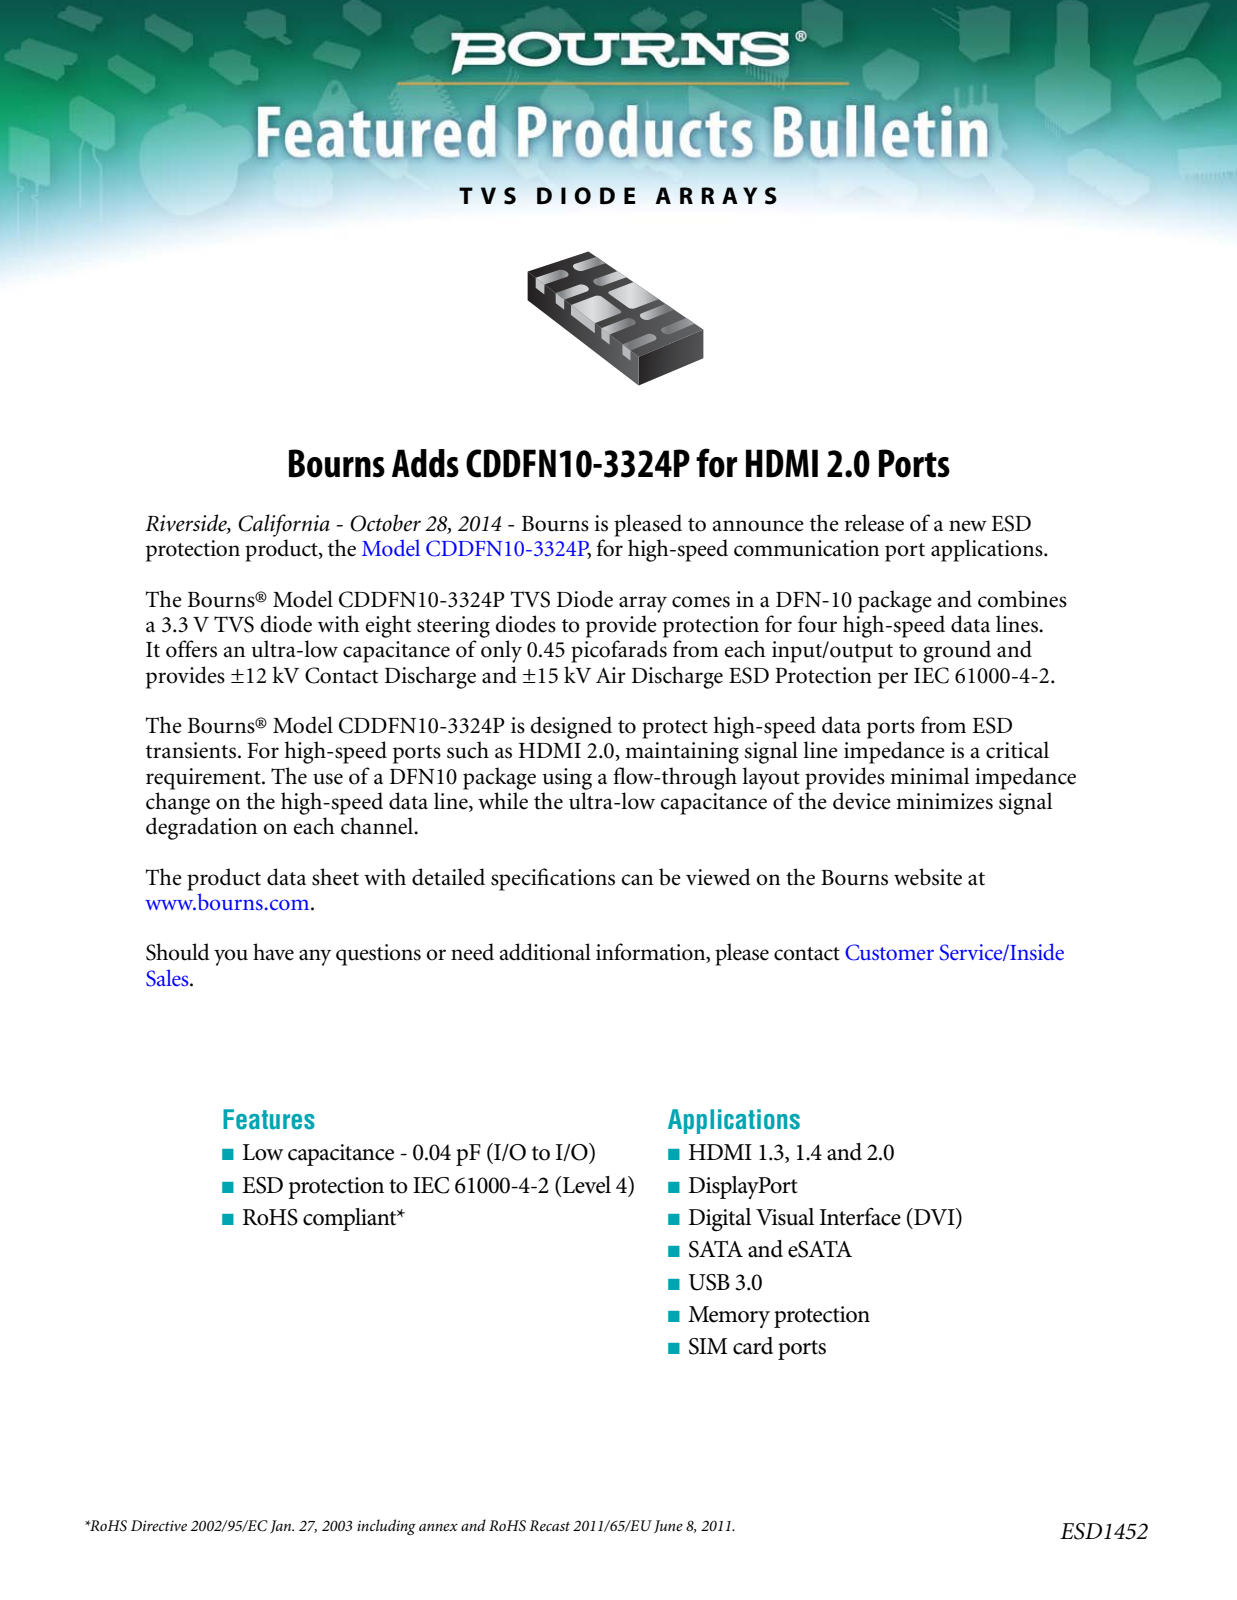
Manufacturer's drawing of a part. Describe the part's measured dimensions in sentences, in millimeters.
The part is named "CDDFN10-0524P". Its 3-D file was written by "PRO/ENGINEER BY PARAMETRIC TECHNOLOGY CORPORATION, 2010100 (CONFIG_CONTROL_DESIGN)". It is 1 solid with 54 faces: 43 planar, 11 cylindrical and 0 other. Overall it measures 2.5 by 1 by 0.57 millimeters. Its volume is 1 cubic millimeters and its surface area 9 square millimeters. Partial cylindrical surfaces (rounded edges, fillets, slot ends): 9 of radius 0.1. The main face-to-face distances are 0.55, 1, 0.58, 2.5, 0.7, 0.5, 1.5, 1.3, 0.4, 0.8.
